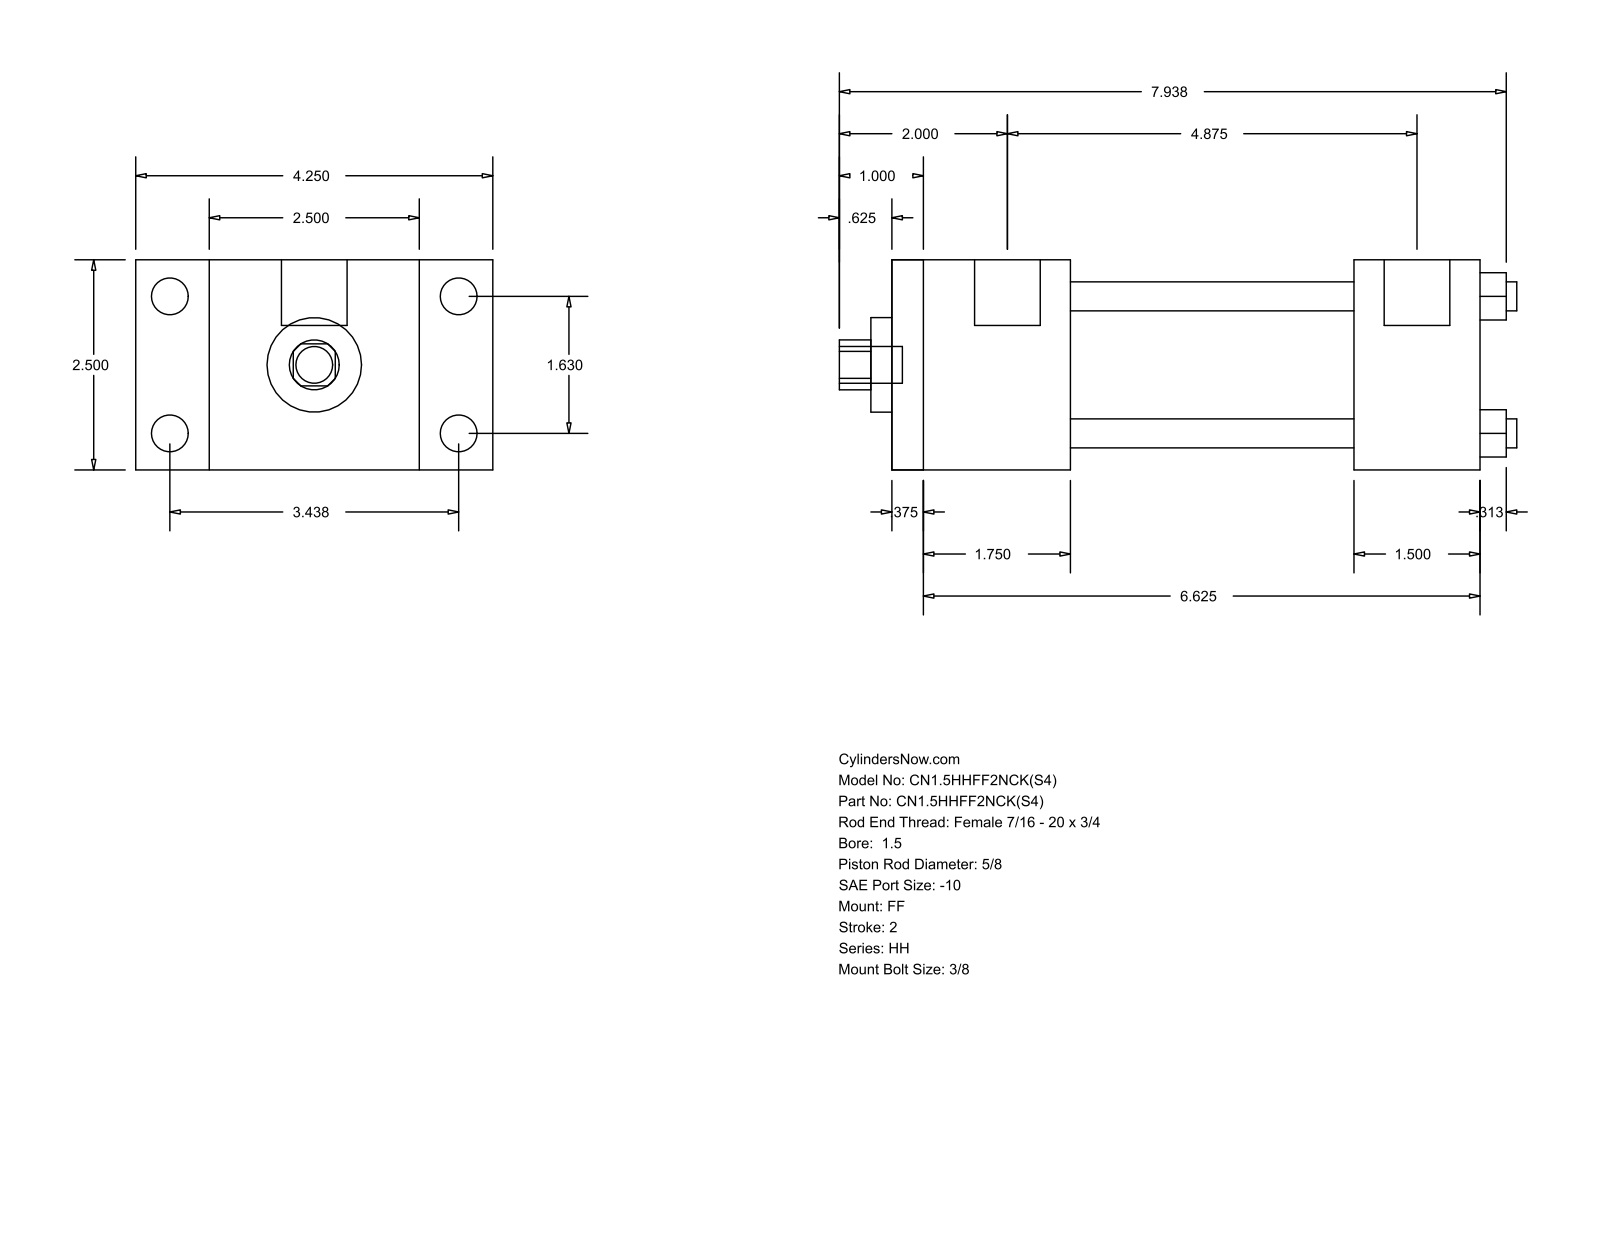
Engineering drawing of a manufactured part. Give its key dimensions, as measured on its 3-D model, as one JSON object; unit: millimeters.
{"part_name": "HH_FF__0150_0.625", "step_written_by": "GSSL Pune (CONFIG_CONTROL_DESIGN)", "units": "millimeters", "bodies": {"solids": 0, "faces": 92, "planar": 64, "cylindrical": 28, "other": 0}, "overall_size": [204.79, 107.95, 63.5], "round_holes": [[8.76, 4], [15.88, 1], [28.57, 1], [44.45, 1]], "round_bosses_or_shafts": [[11.13, 4], [5.56, 4], [19.84, 2], [11.11, 1]], "partial_cylinders_radius": [[7.54, 1]], "face_to_face_distances": [63.5, 177.8, 9.52, 168.28, 53.97, 44.45, 123.83, 139.69, 130.17, 85.72], "hole_center_spacings": [29.27, 41.4, 58.55]}
